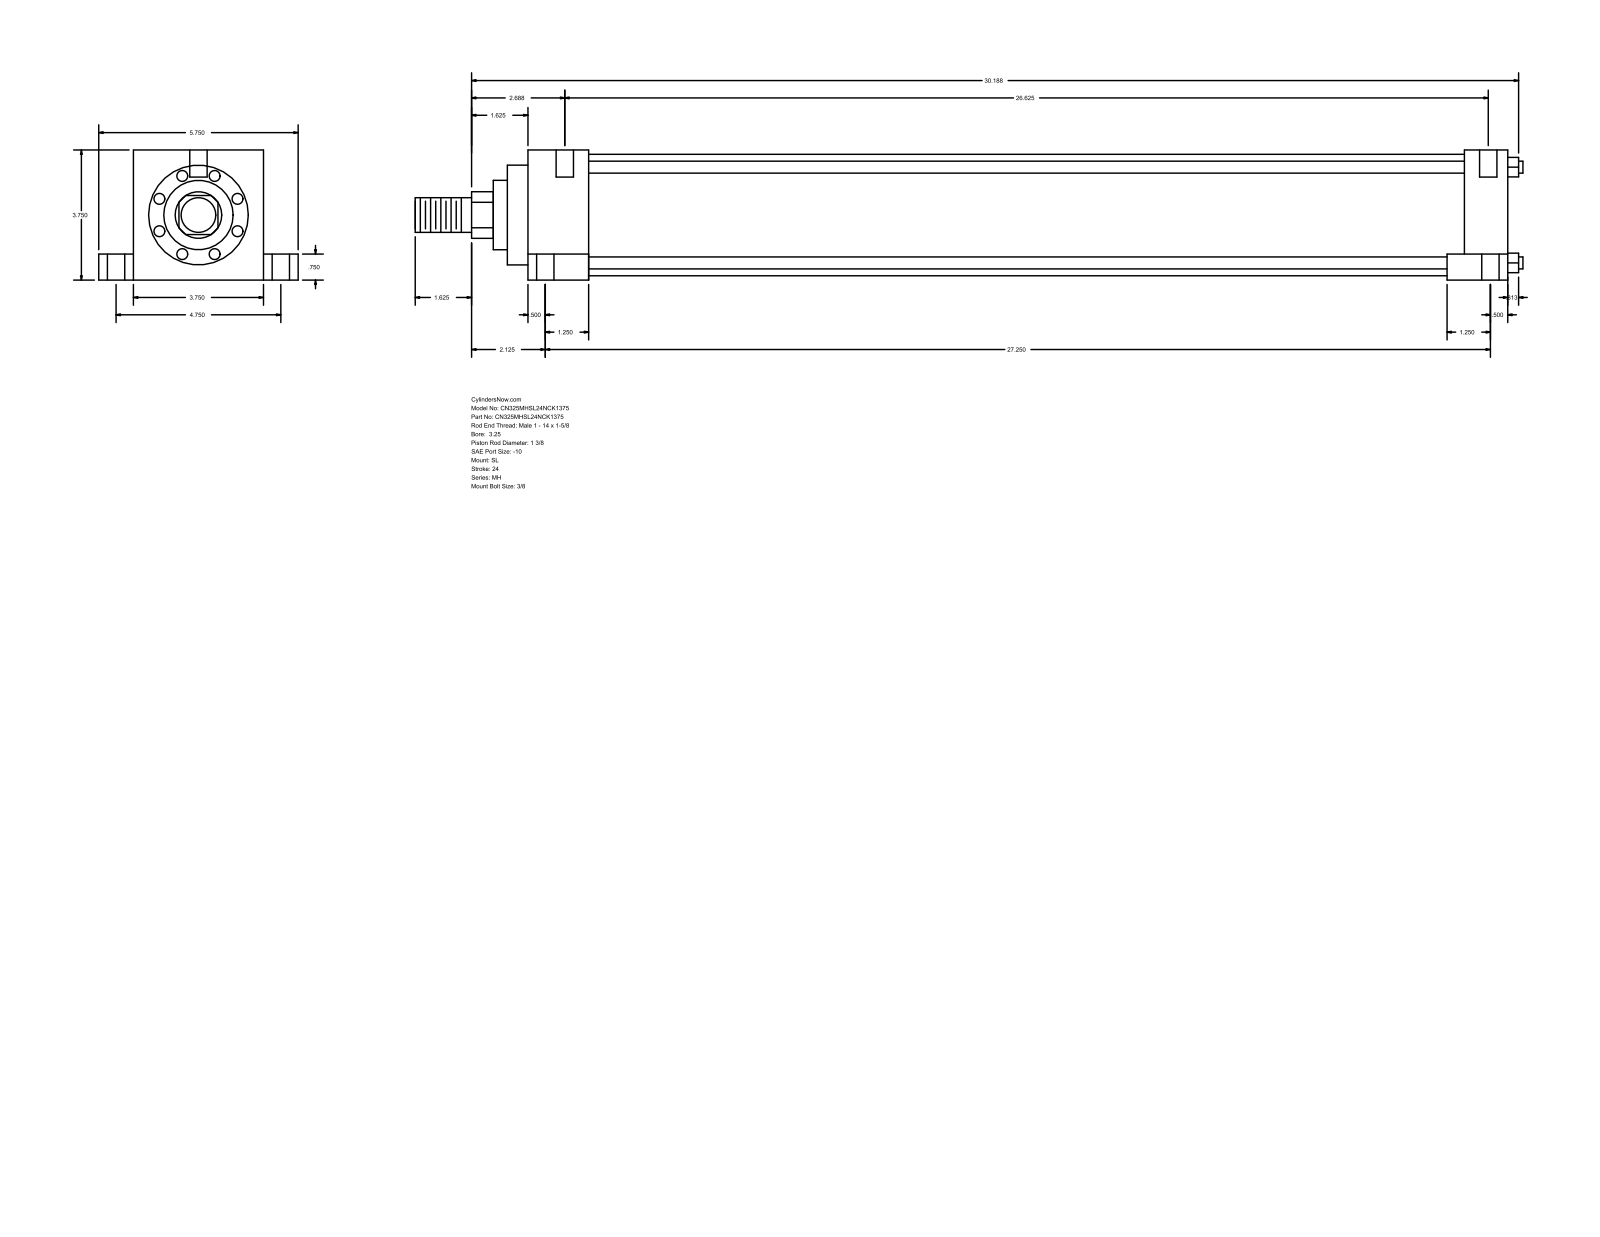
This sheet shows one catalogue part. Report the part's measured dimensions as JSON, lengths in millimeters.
{"part_name": "MH_SL__0325_1.375", "step_written_by": "GSSL Pune (CONFIG_CONTROL_DESIGN)", "units": "millimeters", "bodies": {"solids": 0, "faces": 110, "planar": 77, "cylindrical": 33, "other": 0}, "overall_size": [811.21, 146.05, 95.25], "round_holes": [[12.7, 6], [5.56, 4], [19.05, 4]], "round_bosses_or_shafts": [[8.76, 4], [88.9, 1], [73.03, 1], [50.8, 1], [34.92, 1], [25.4, 1]], "partial_cylinders_radius": [[17.06, 1]], "face_to_face_distances": [95.24, 717.56, 44.45, 673.11, 25.41, 120.65, 19.05, 76.19, 685.81, 641.36], "hole_center_spacings": [60.35, 60.41, 61.65, 62, 120.66, 680.54, 682.12, 682.63]}
